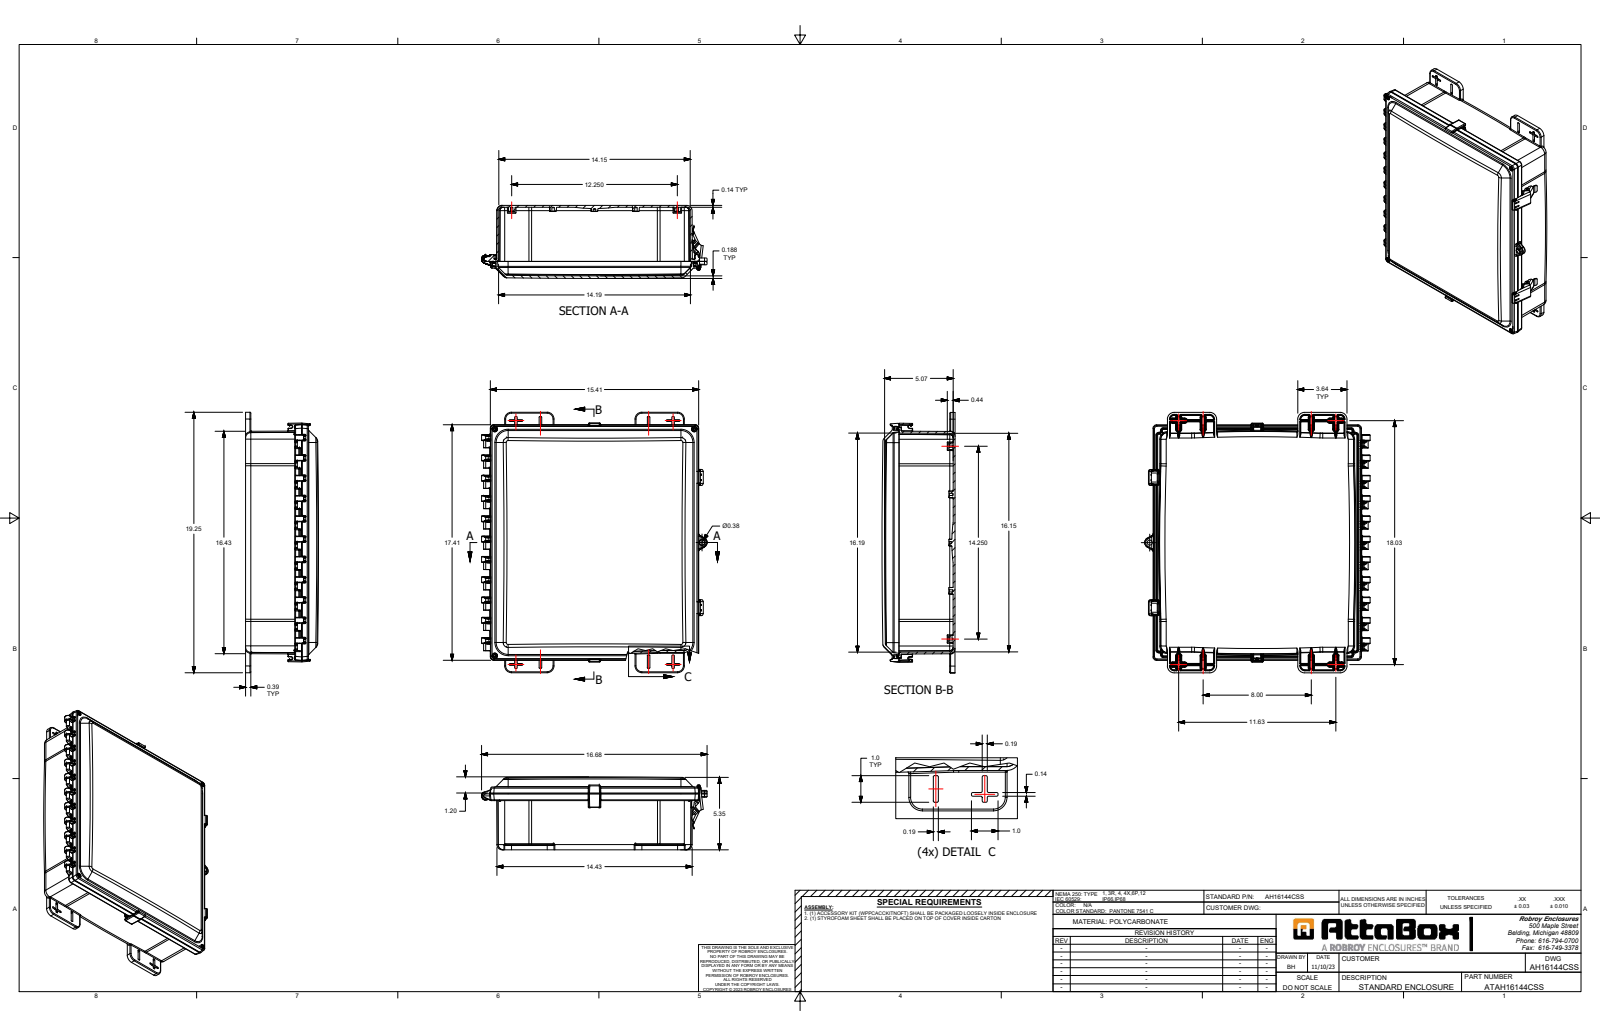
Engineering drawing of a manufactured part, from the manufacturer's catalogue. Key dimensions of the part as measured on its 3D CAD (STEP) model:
Part name (STEP PRODUCT): AH16144SS
STEP written by: SolidWorks 2023 (AUTOMOTIVE_DESIGN)
Units: inches
Bodies: 10 solids, 1262 faces (565 planar, 406 cylindrical, 291 other)
Overall size (bounding box): 19.25 × 16.676 × 5.399
Volume: 146.6 in³ · Surface area: 1 785 in²
Round holes (diameter × count): ⌀0.187 ×21, ⌀0.195 ×4, ⌀0.25 ×4, ⌀0.296 ×4, ⌀0.39 ×4, ⌀0.14 ×1, ⌀0.209 ×1, ⌀0.327 ×1, ⌀0.375 ×1, ⌀0.45 ×1
Round bosses / shafts (diameter × count): ⌀0.487 ×21, ⌀0.625 ×4, ⌀0.313 ×1, ⌀0.24 ×1, ⌀0.199 ×1, ⌀0.15 ×1, ⌀0.12 ×1
Partial cylindrical surfaces — rounded edges, fillets, slot ends (radius × count): R0.035 ×85, R0.065 ×18, R0.05 ×16, R0.039 ×12, R0.1 ×11, R0.15 ×8, R0.5 ×8, R5.14 ×8
Main face-to-face distances: 0.14, 14.247, 0.5, 0.501, 0.187, 4, 16.243, 4.14, 3.64, 3.5
Hole centre spacings: 4.698, 7.085, 7.755, 9.396, 9.854, 11.626, 12.318, 3.062
